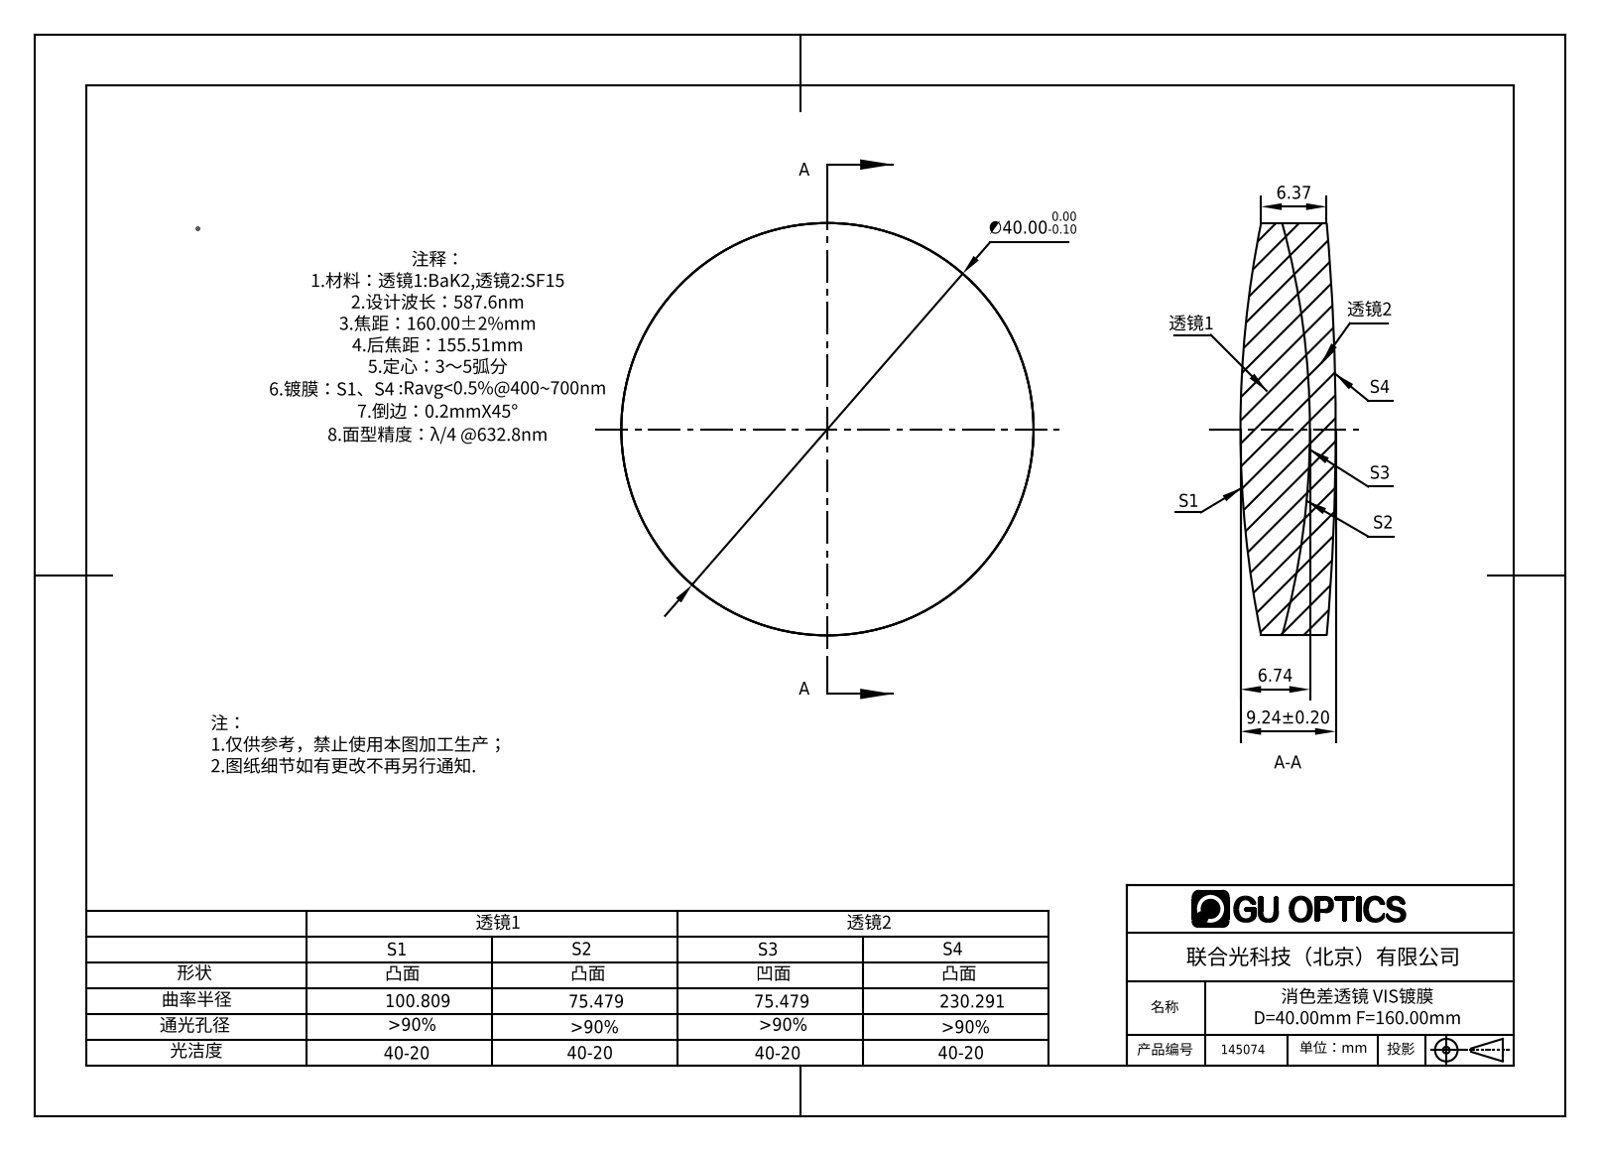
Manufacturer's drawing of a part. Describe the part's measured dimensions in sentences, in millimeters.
The part is named "145074". Its 3-D file was written by "SolidWorks 2016 (AUTOMOTIVE_DESIGN)". It is 2 solids with 12 faces: 0 planar, 4 cylindrical and 8 other. Overall it measures 40 by 40 by 9.24 millimeters. Its volume is 9 810 cubic millimeters and its surface area 5 887 square millimeters. Round bosses or shafts: 1 of diameter 40.
